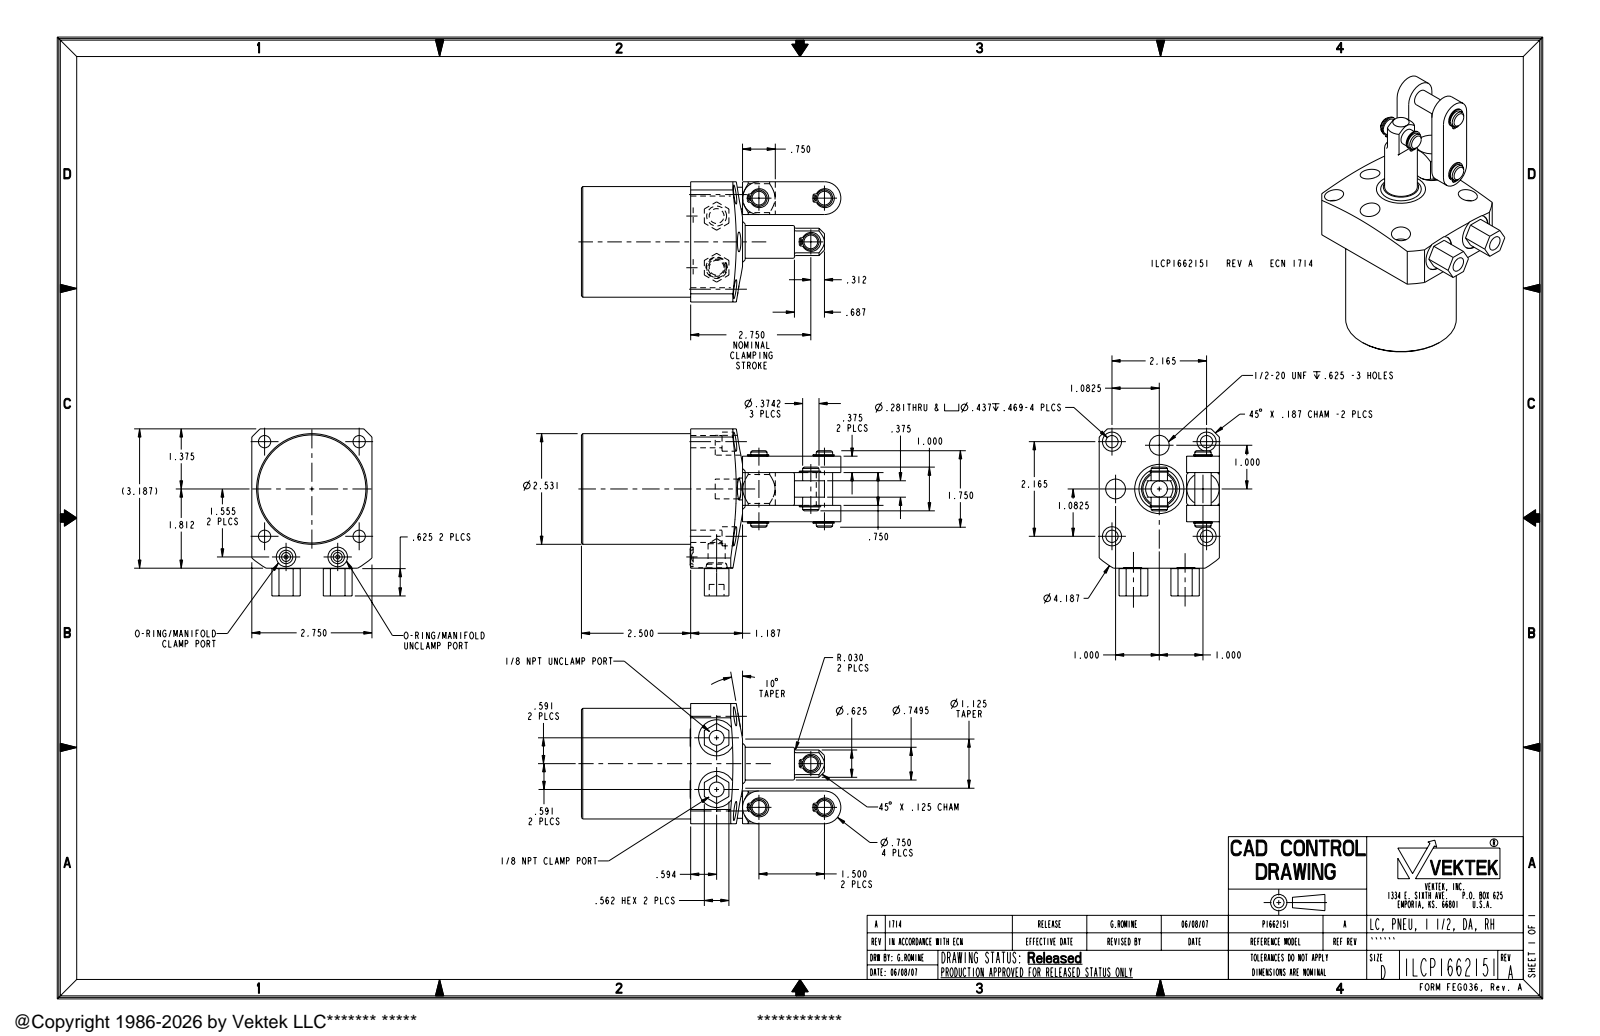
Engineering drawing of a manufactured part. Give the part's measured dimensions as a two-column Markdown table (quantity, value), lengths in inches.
| quantity | value |
| --- | --- |
| part name | ILCP1662151 |
| STEP written by | PRO/ENGINEER BY PARAMETRIC TECHNOLOGY CORPORATION, 2005180 (AUTOMOTIVE_DESIGN_CC2) |
| units | inches |
| bodies | 3 solids, 298 faces (120 planar, 130 cylindrical, 48 other) |
| overall size | 5.937 × 3.822 × 2.75 |
| volume | 24.02 in³ |
| surface area | 78.33 in² |
| round holes (diameter × count) | 0.041 × 6, 0.281 × 4, 0.437 × 4, 0.339 × 2, 0.392 × 2, 0.447 × 2, 0.453 × 2, 0.825 × 2 |
| round bosses / shafts (diameter × count) | 0.433 × 3, 0.374 × 3, 0.437 × 2, 2.531 × 1, 0.75 × 1, 0.5 × 1 |
| partial cylindrical surfaces (radius × count) | 0.041 × 12, 0.375 × 2, 0.313 × 1, 0.5 × 1, 2.094 × 1 |
| main face-to-face distances | 2.5, 2.75, 1.125, 0.375, 0.75, 0.625, 1.5, 2.125, 1.75, 0.562 |
| hole center spacings | 1.086, 2.165, 2.347, 0.098, 0.682, 1.048, 1.182, 1.5 |
